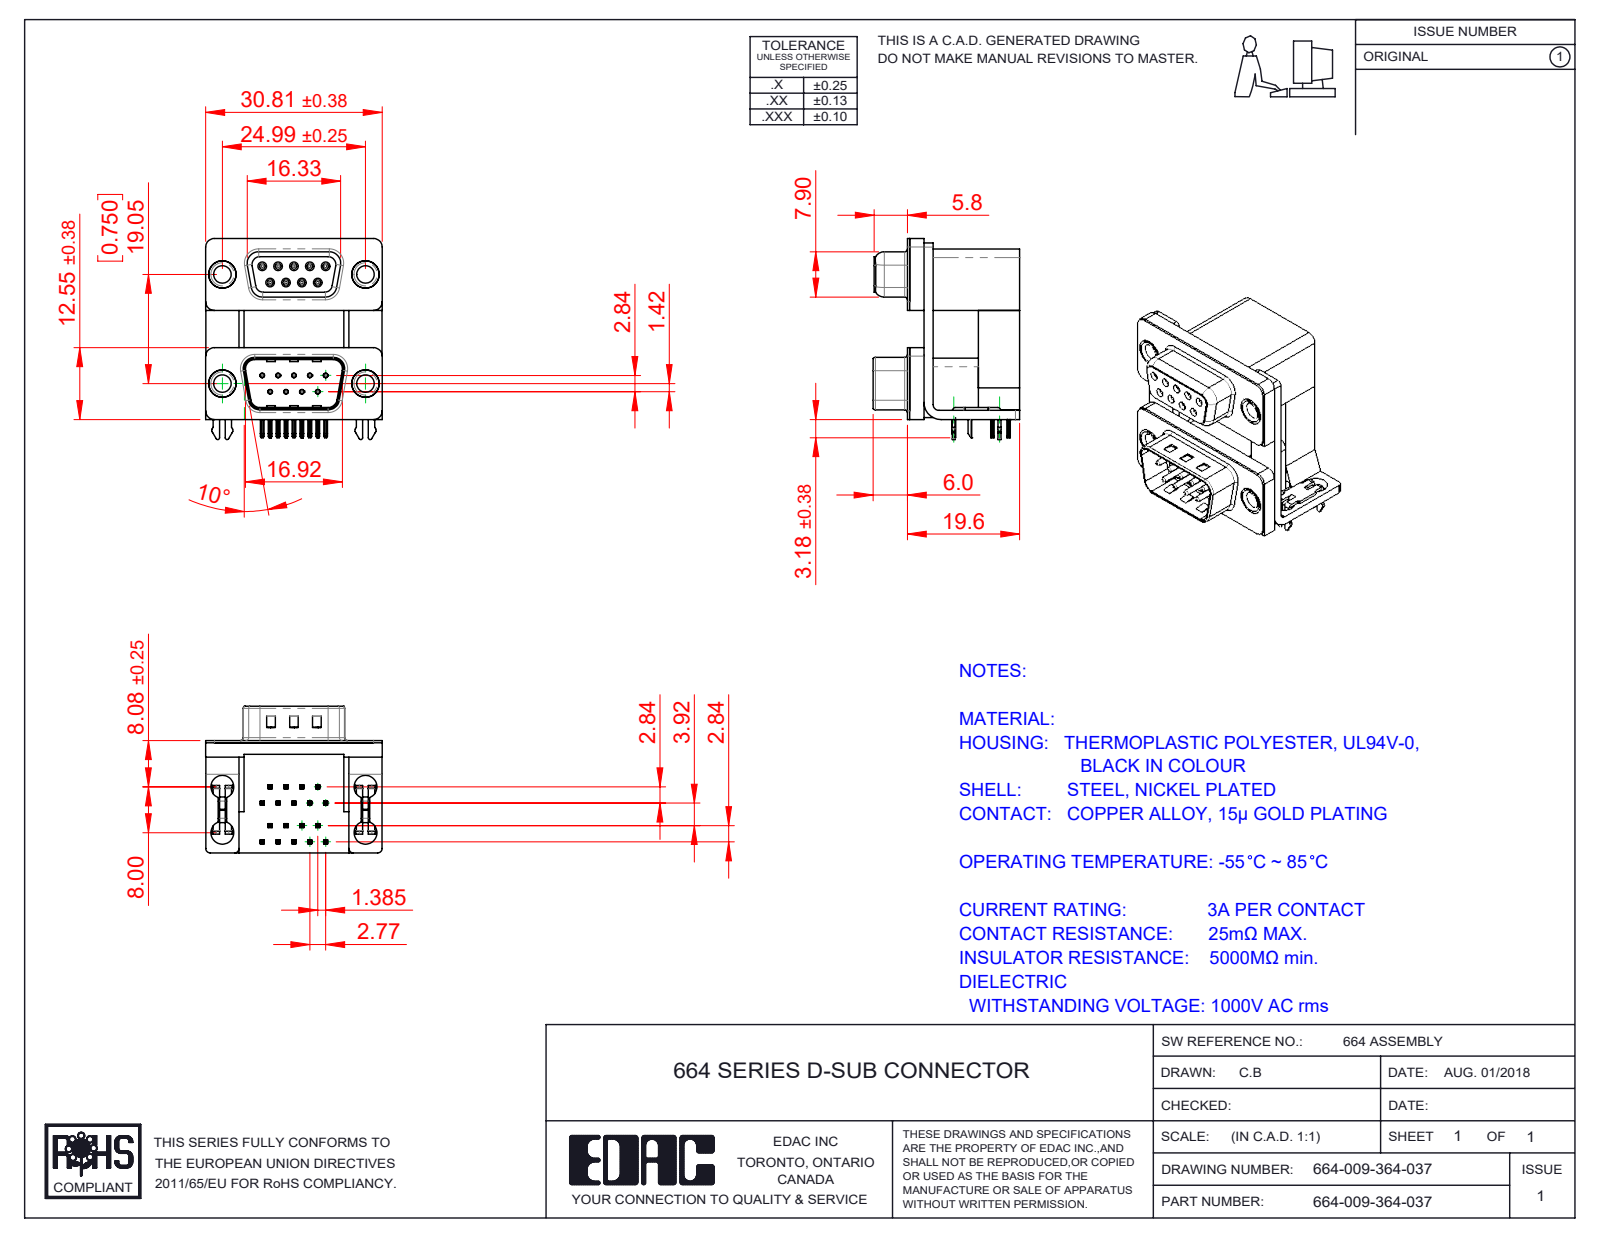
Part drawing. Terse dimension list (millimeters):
name: 664 Housing Lower_09 Contacts; 664 Thru Hole Rivet; 664 Contact Top Lower; 664 Mounting Bracket_2ProngM (+8 more)
written by: SolidWorks 2020 (CONFIG_CONTROL_DESIGN)
unit: mm
bodies: 31 solids, 2597 faces (1365 planar, 709 cylindrical, 523 other)
size: 35.1 × 30.81 × 25.6
volume: 10 754 mm³; area: 12 749 mm²
holes: 18× ⌀0.8, 9× ⌀0.35, 9× ⌀0.9, 8× ⌀4, 4× ⌀3.05, 4× ⌀3.5, 4× ⌀4.8, 4× ⌀5
bosses: 9× ⌀1.2, 9× ⌀0.75, 4× ⌀4.9, 4× ⌀4.75, 4× ⌀3.85
rounds: 74× R0.1, 46× R0.25, 36× R0.15, 18× R0.12, 18× R0.35, 16× R0.5, 13× R1.5, 10× R0.75
face distances: 0.4, 2.5, 16.7, 19.2, 7.2, 9.5, 12, 1.6, 19.6, 12.4
hole spacings: 3.16, 2.77, 19.25, 19.05, 5.54, 19.84, 16.27, 21.93
